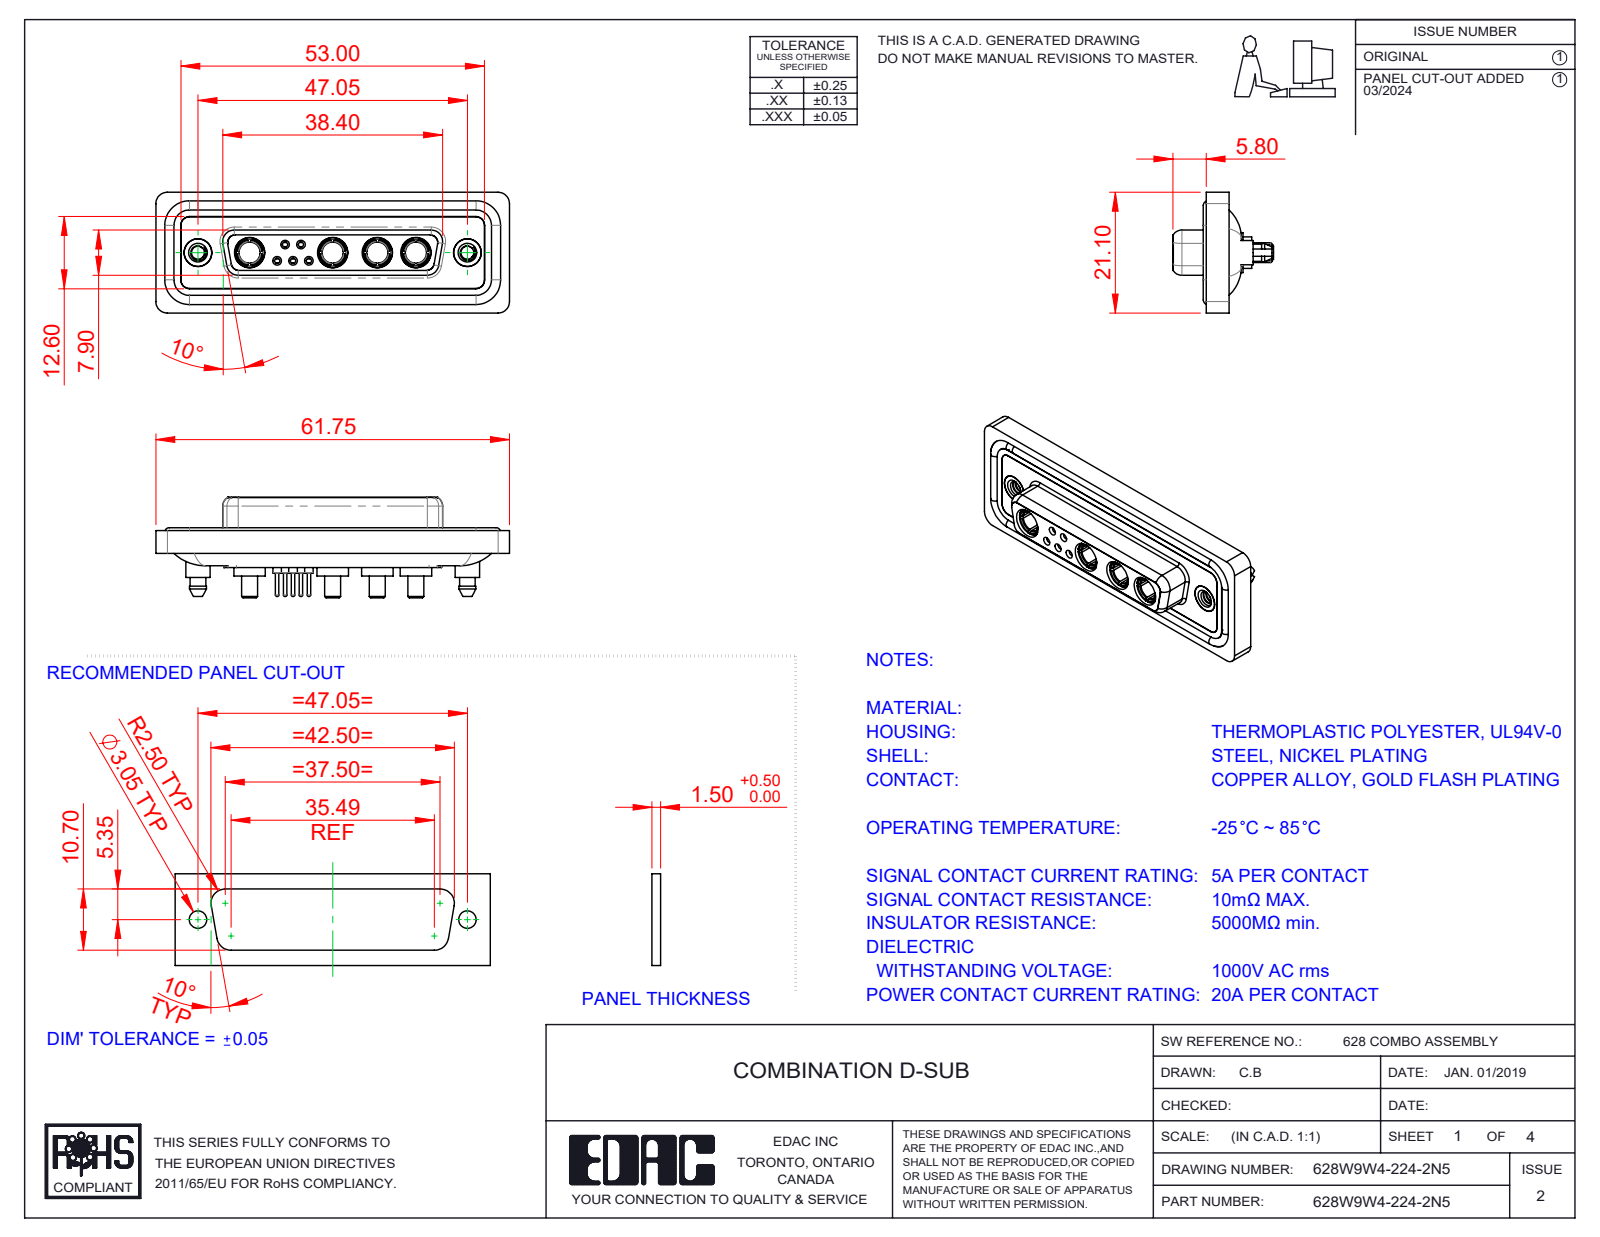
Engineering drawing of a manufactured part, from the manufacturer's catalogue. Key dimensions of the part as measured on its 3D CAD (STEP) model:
Part name (STEP PRODUCT): 628W9W4-224-2N5; 628Combo Shell Rear_25 Contacts; Power Socket_20A S; 628Combo Housing_9W4 (+5 more)
STEP written by: SolidWorks 2023 (CONFIG_CONTROL_DESIGN)
Units: millimetres
Bodies: 20 solids, 1007 faces (312 planar, 407 cylindrical, 288 other)
Overall size (bounding box): 61.75 × 21.1 × 17.55
Volume: 8 357 mm³ · Surface area: 13 895 mm²
Round holes (diameter × count): ⌀4.85 ×6, ⌀0.9 ×5, ⌀1.1 ×5, ⌀1.5 ×5, ⌀2 ×5, ⌀3.7 ×4, ⌀5.3 ×4, ⌀1.6 ×3, ⌀1.7 ×2, ⌀2.26 ×2, ⌀4 ×2, ⌀4.05 ×2
Round bosses / shafts (diameter × count): ⌀1.6 ×6, ⌀2.2 ×5, ⌀0.6 ×5, ⌀5.5 ×4, ⌀5.2 ×4, ⌀4.96 ×4, ⌀4.75 ×4, ⌀3.75 ×4
Partial cylindrical surfaces — rounded edges, fillets, slot ends (radius × count): R1.5 ×24, R2 ×18, R1.6 ×10, R1.35 ×8, R0.25 ×4, R0.5 ×4, R0.6 ×4, R0.65 ×4
Main face-to-face distances: 0.4, 1.8, 7.45, 5.65, 0.5, 7.05, 6.6, 1.6, 1.1, 2.9
Hole centre spacings: 3.16, 2.77, 5.03, 2.76, 4.4, 5.02, 5.54, 5.73
